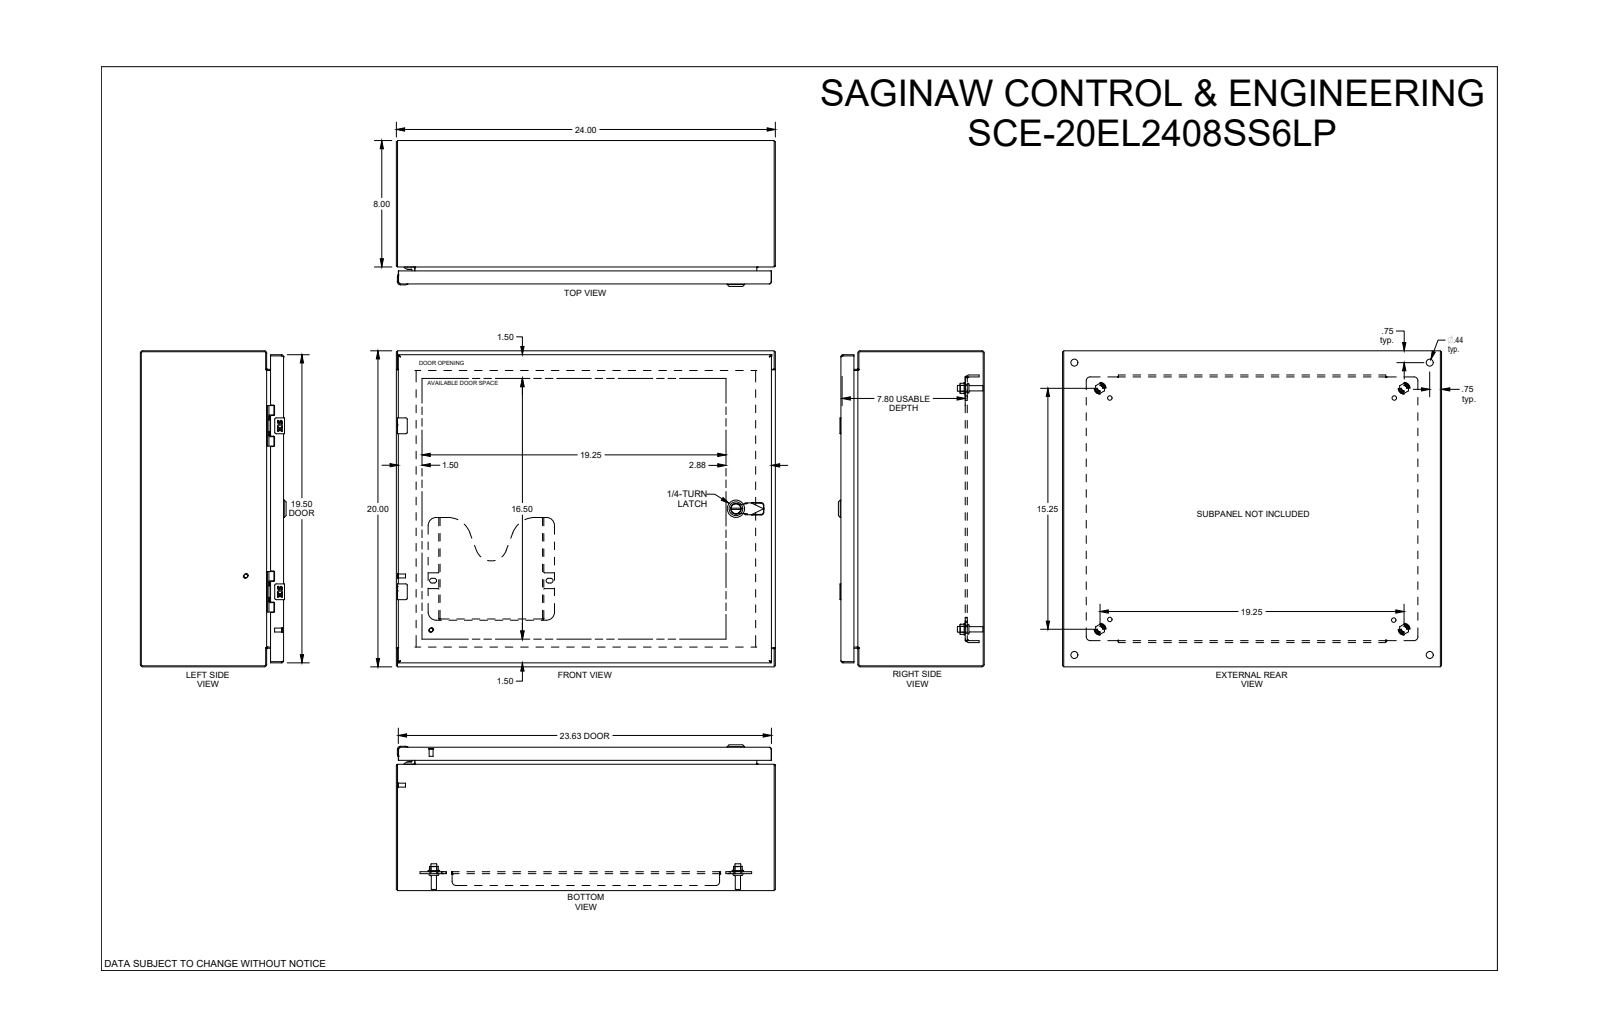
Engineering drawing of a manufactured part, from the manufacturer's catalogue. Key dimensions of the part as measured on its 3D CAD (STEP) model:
Part name (STEP PRODUCT): SCE-20EL2408LP
STEP written by: SolidWorks 2021 (AUTOMOTIVE_DESIGN)
Units: inches
Bodies: 24 solids, 1257 faces (560 planar, 486 cylindrical, 211 other)
Overall size (bounding box): 24 × 20 × 9.935
Volume: 200.3 in³ · Surface area: 4 827 in²
Round holes (diameter × count): ⌀0.172 ×4, ⌀0.205 ×4, ⌀0.244 ×4, ⌀0.281 ×4, ⌀0.375 ×4, ⌀0.437 ×4, ⌀0.5 ×4, ⌀0.04 ×2, ⌀0.188 ×2, ⌀0.218 ×2, ⌀0.197 ×1, ⌀0.204 ×1
Round bosses / shafts (diameter × count): ⌀0.375 ×4, ⌀0.33 ×4, ⌀0.25 ×4, ⌀0.248 ×4, ⌀0.24 ×4, ⌀1.102 ×1, ⌀0.78 ×1, ⌀0.63 ×1
Partial cylindrical surfaces — rounded edges, fillets, slot ends (radius × count): R0.015 ×24, R0.04 ×17, R0.22 ×16, R0.043 ×12, R0.118 ×12, R0.031 ×10, R0.06 ×9, R0.062 ×8
Main face-to-face distances: 0.075, 0.06, 8.993, 9.068, 9.008, 8.933, 19.925, 1, 0.125, 1.075
Hole centre spacings: 0.494, 0.875, 10.5, 20.944, 18.641, 0.984, 2.346, 2.348
